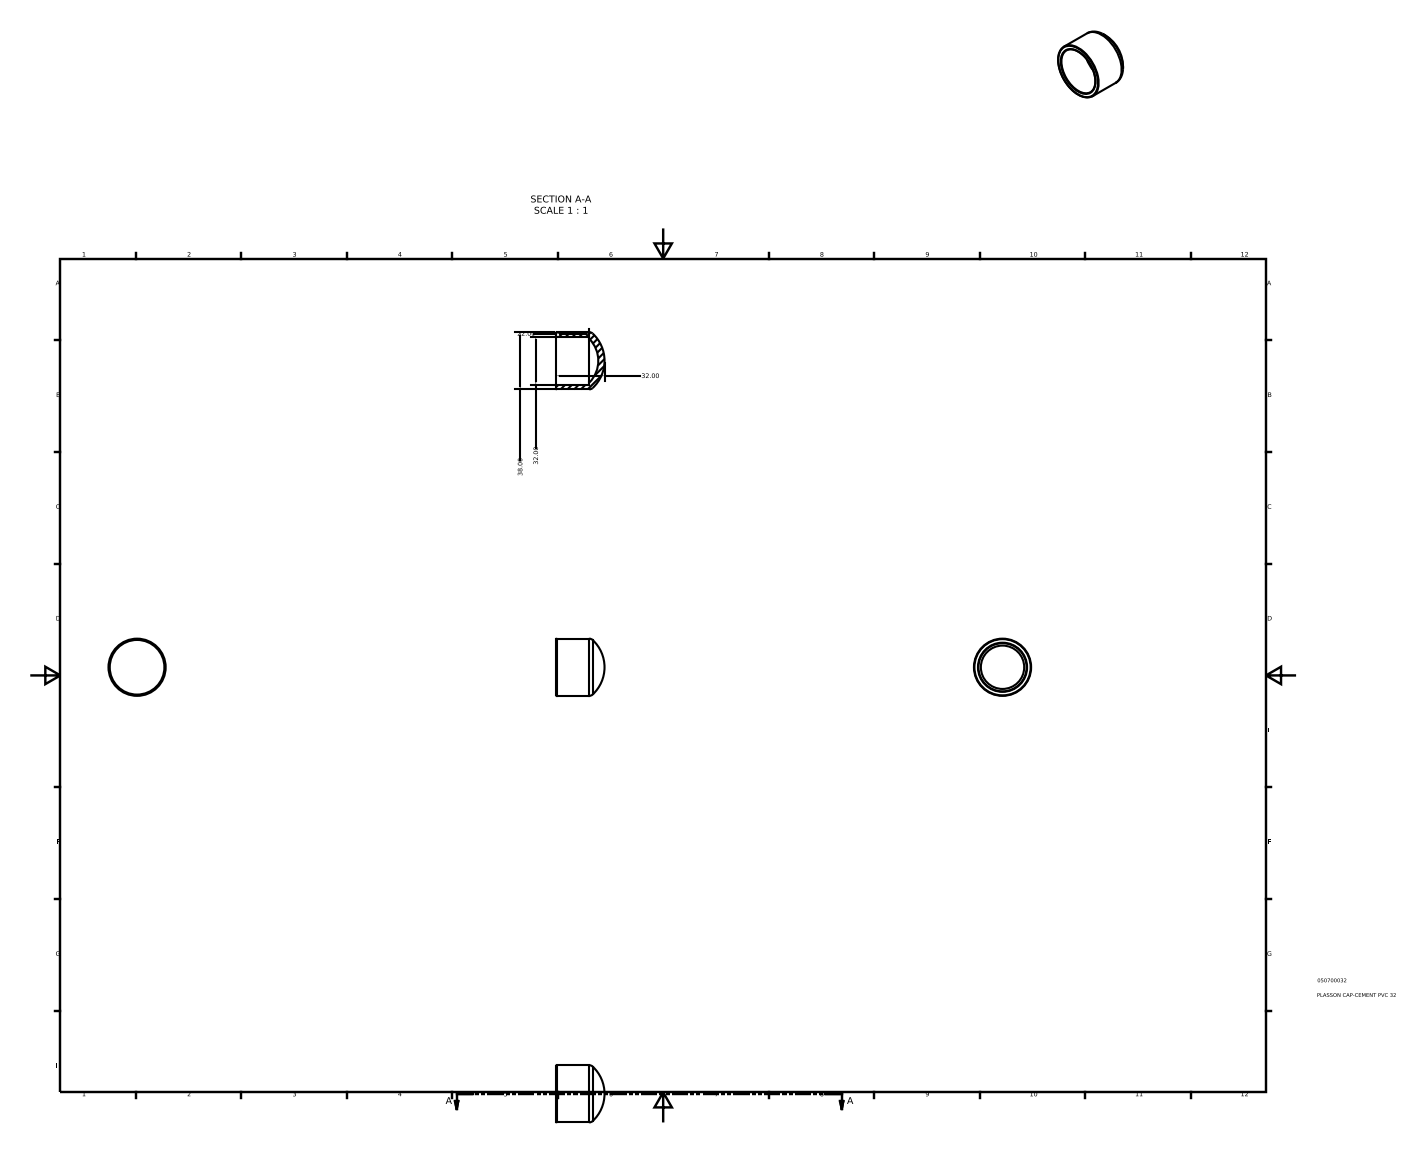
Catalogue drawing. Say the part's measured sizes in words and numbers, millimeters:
The part is named "050700032". Its 3-D file was written by "Autodesk Inventor 2015 (AUTOMOTIVE_DESIGN)". It is 1 solid with 9 faces: 2 planar, 2 cylindrical and 5 other. Overall it measures 38 by 38 by 32 millimeters. Its volume is 11 877 cubic millimeters and its surface area 7 551 square millimeters. Round holes: 1 of diameter 32. Round bosses or shafts: 1 of diameter 38. The main face-to-face distances are 22.
